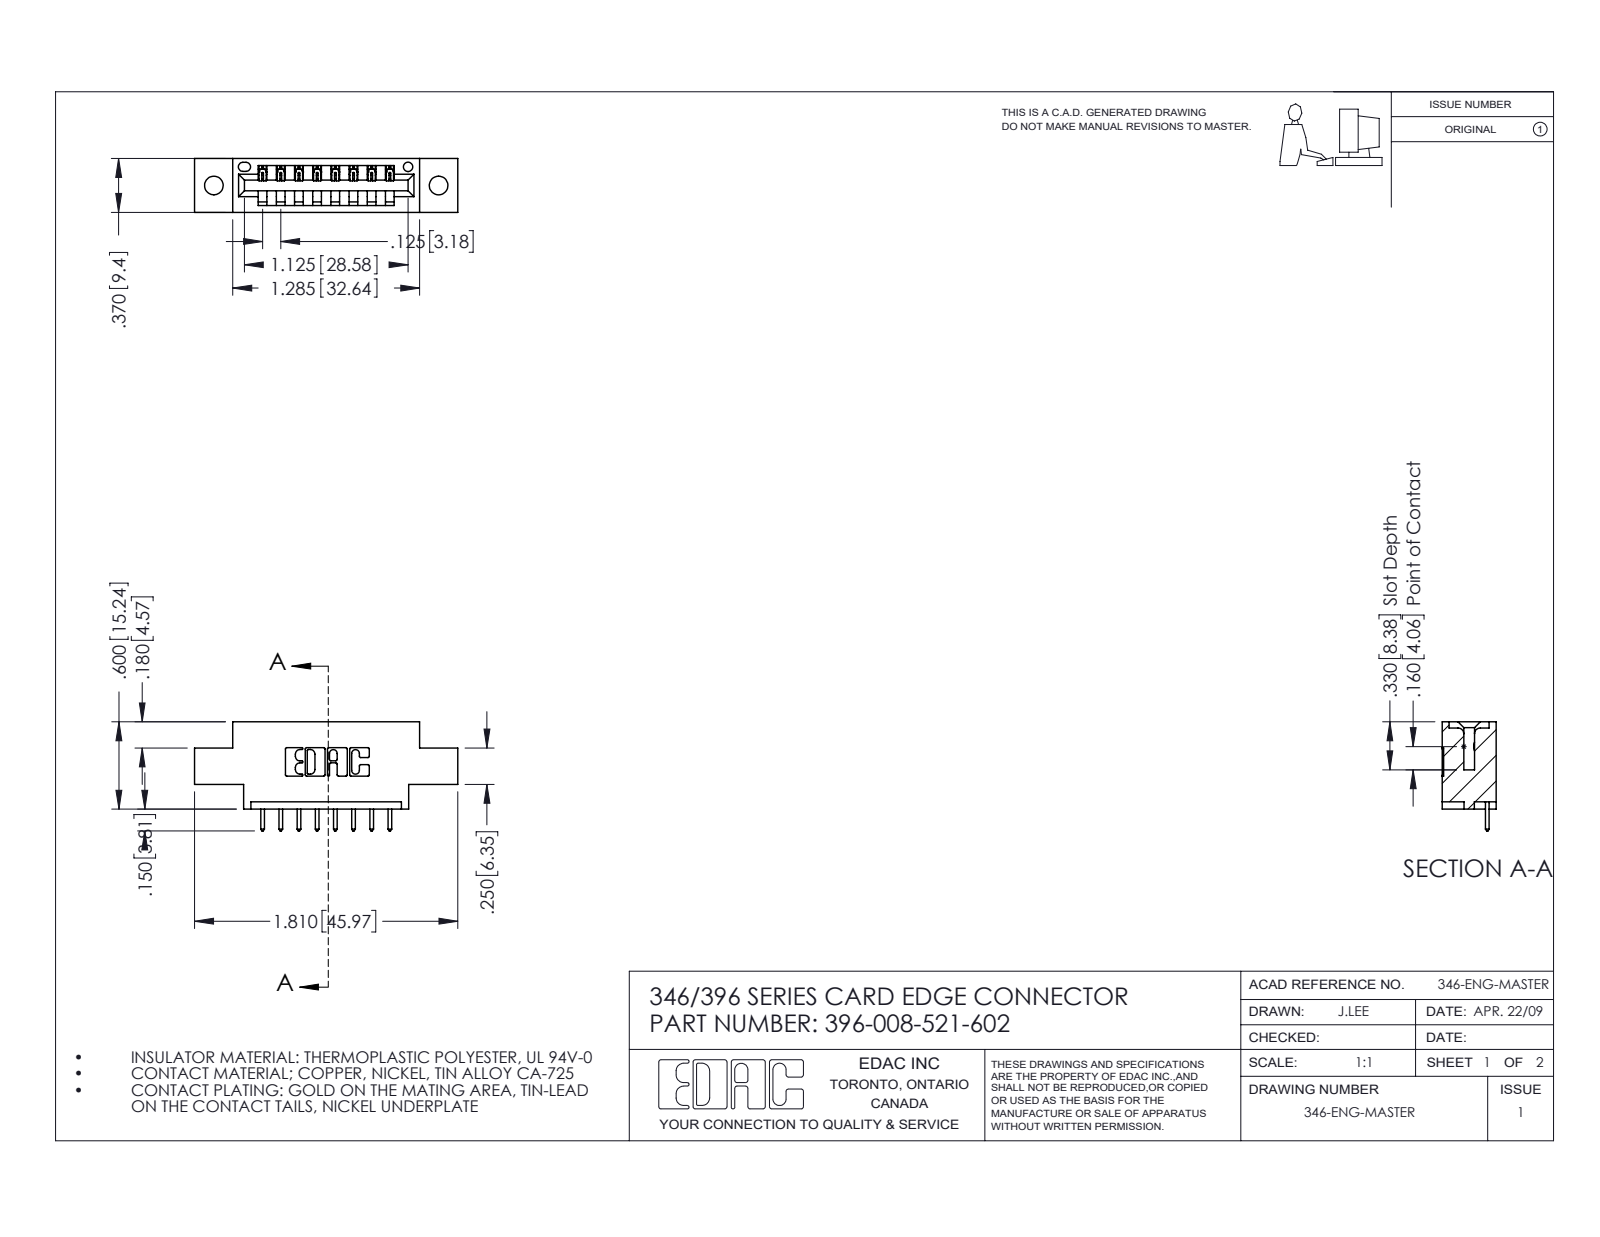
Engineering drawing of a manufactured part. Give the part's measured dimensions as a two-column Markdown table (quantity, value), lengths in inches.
| quantity | value |
| --- | --- |
| part name | 396-008-521-602; 345-292-001_345-293-121; 346 Part_0.170 Offset - 0.128 Dia |
| STEP written by | SolidWorks 2016 (CONFIG_CONTROL_DESIGN) |
| units | inches |
| bodies | 9 solids, 590 faces (400 planar, 190 cylindrical, 0 other) |
| overall size | 1.81 × 0.75 × 0.37 |
| volume | 0.241 in³ |
| surface area | 6.776 in² |
| round holes (diameter × count) | 0.128 × 2, 0.064 × 1 |
| partial cylindrical surfaces (radius × count) | 0.01 × 22, 0.006 × 16, 0.01 × 16, 0.007 × 6, 0.031 × 6, 0.026 × 3, 0.031 × 2, 0.04 × 2 |
| main face-to-face distances | 0.25, 0.37, 0.048, 0.322, 0.148, 0.222, 0.1, 0.174, 0.072, 0.298 |
| hole center spacings | 0.246, 1.341, 1.545 |
